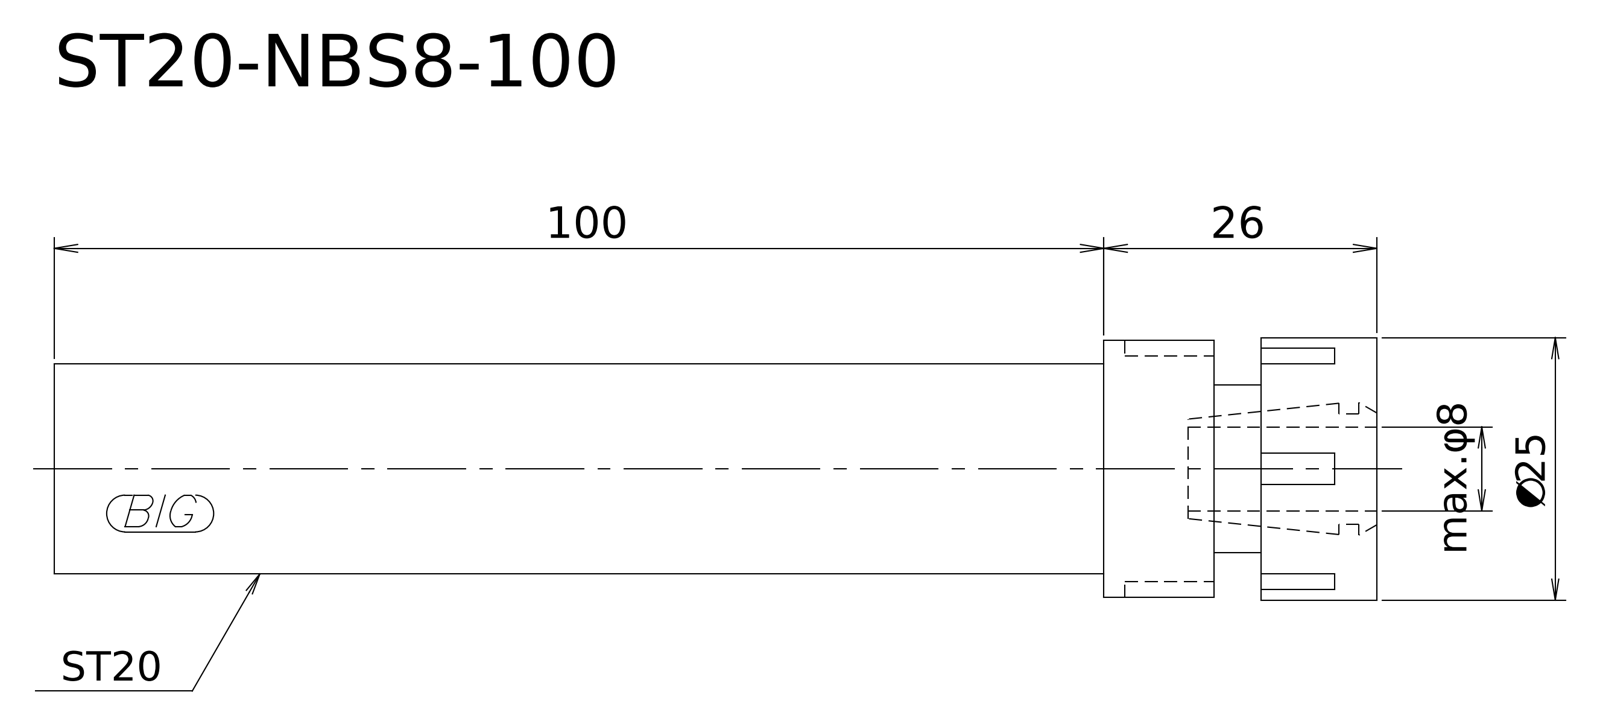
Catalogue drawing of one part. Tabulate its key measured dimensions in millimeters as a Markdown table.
| quantity | value |
| --- | --- |
| STEP written by | Kubotek KeyCreator V8.5.1 (14335) (CONFIG_CONTROL_DESIGN) |
| units | millimeters |
| bodies | 1 solid, 9 faces (5 planar, 4 cylindrical, 0 other) |
| overall size | 126 × 25 × 25 |
| volume | 42 670 mm³ |
| surface area | 9 704 mm² |
| round bosses / shafts (diameter × count) | 25 × 1, 24.5 × 1, 20 × 1, 16 × 1 |
| main face-to-face distances | 126, 11, 115, 15.5, 4.5, 110.5, 26, 15, 10.5, 100 |
